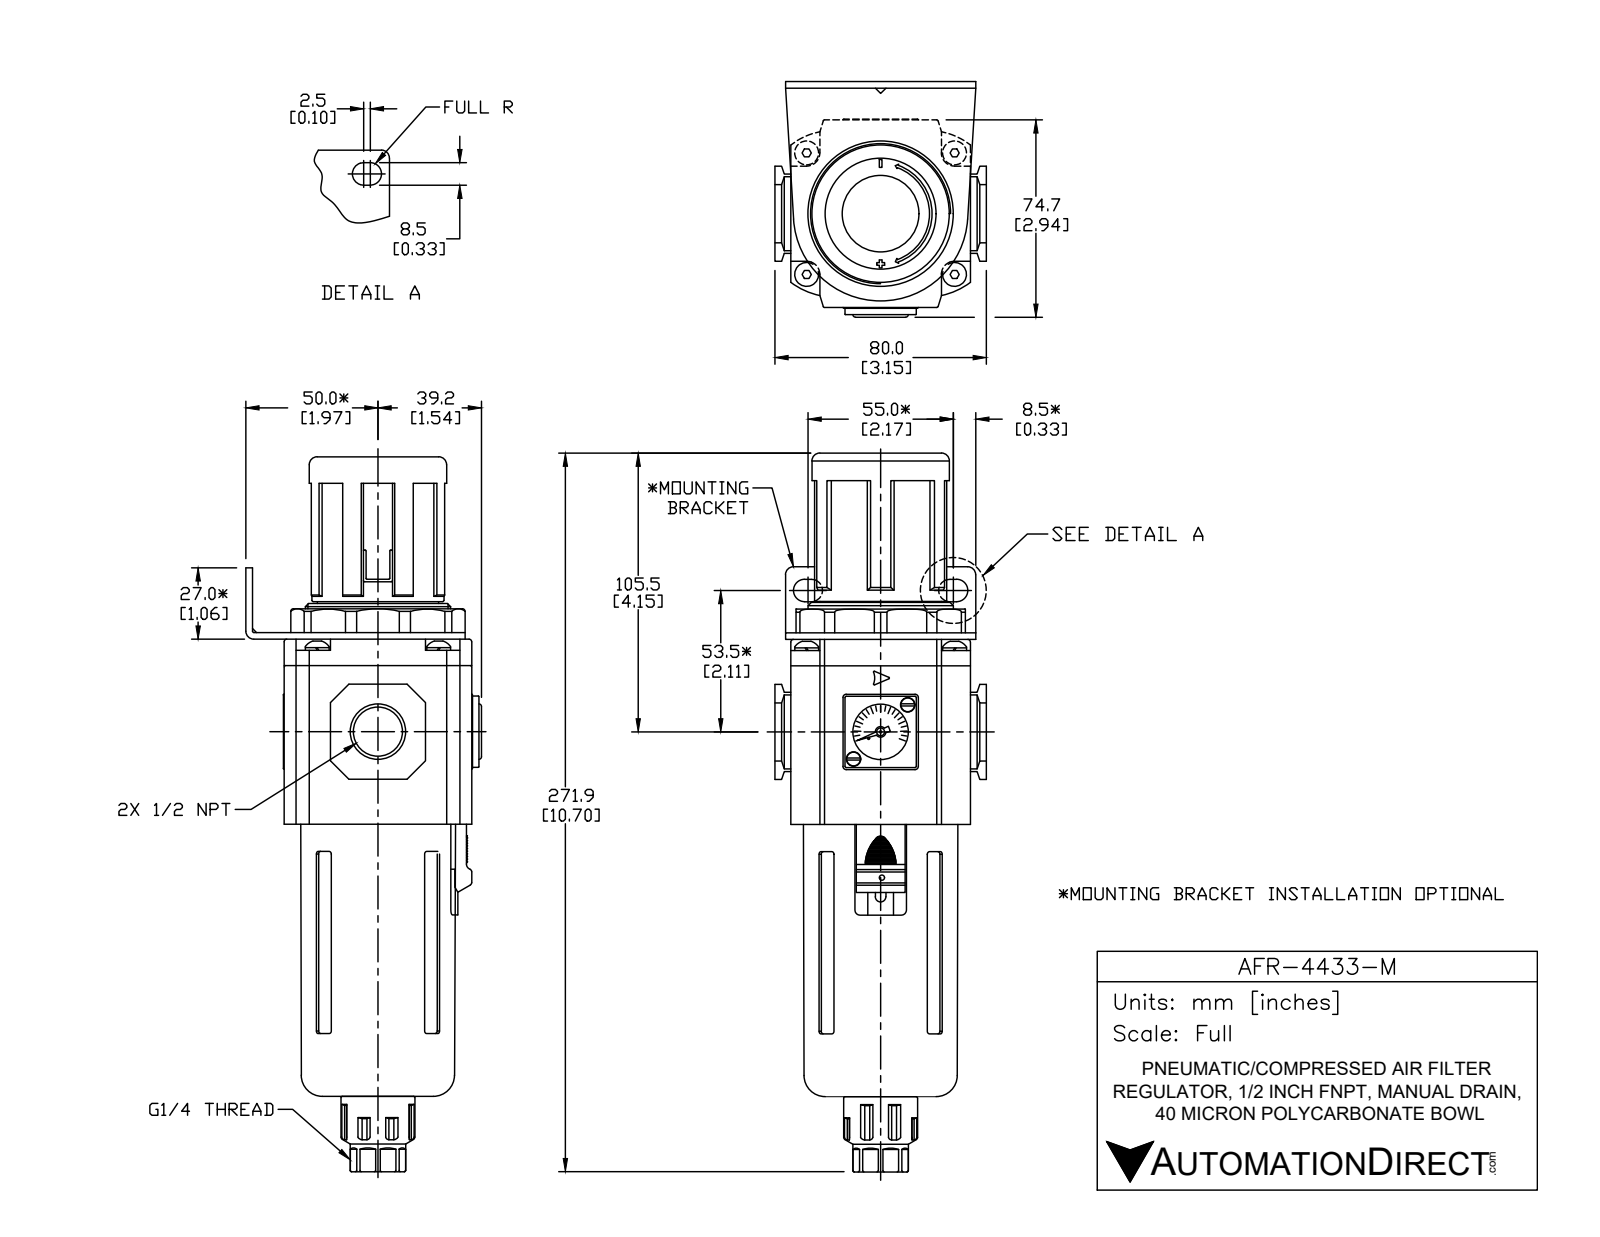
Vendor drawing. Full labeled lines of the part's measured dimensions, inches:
Part name (STEP PRODUCT): AFR-4433-M
STEP written by: SolidWorks 2015 (CONFIG_CONTROL_DESIGN)
Units: inches
Bodies: 16 solids, 606 faces (371 planar, 169 cylindrical, 66 other)
Overall size (bounding box): 10.65 × 3.472 × 3.15
Volume: 34.29 in³ · Surface area: 179.1 in²
Round holes (diameter × count): ⌀0.118 ×6, ⌀0.079 ×1, ⌀0.472 ×1, ⌀0.703 ×1, ⌀0.827 ×1, ⌀1.181 ×1, ⌀1.969 ×1
Round bosses / shafts (diameter × count): ⌀0.354 ×4, ⌀0.106 ×2, ⌀2.283 ×1, ⌀2.165 ×1, ⌀2.047 ×1, ⌀1.72 ×1, ⌀1.102 ×1, ⌀0.827 ×1
Partial cylindrical surfaces — rounded edges, fillets, slot ends (radius × count): R0.114 ×18, R0.039 ×12, R0.047 ×10, R0.02 ×9, R0.374 ×8, R0.012 ×4, R0.167 ×4, R0.248 ×4
Main face-to-face distances: 0.098, 2.756, 2.854, 2.795, 2.677, 2.913, 2.055, 0.157, 3.366, 0.61
Hole centre spacings: 1.311, 0.571, 1.677, 2.016, 2.622, 1.141
